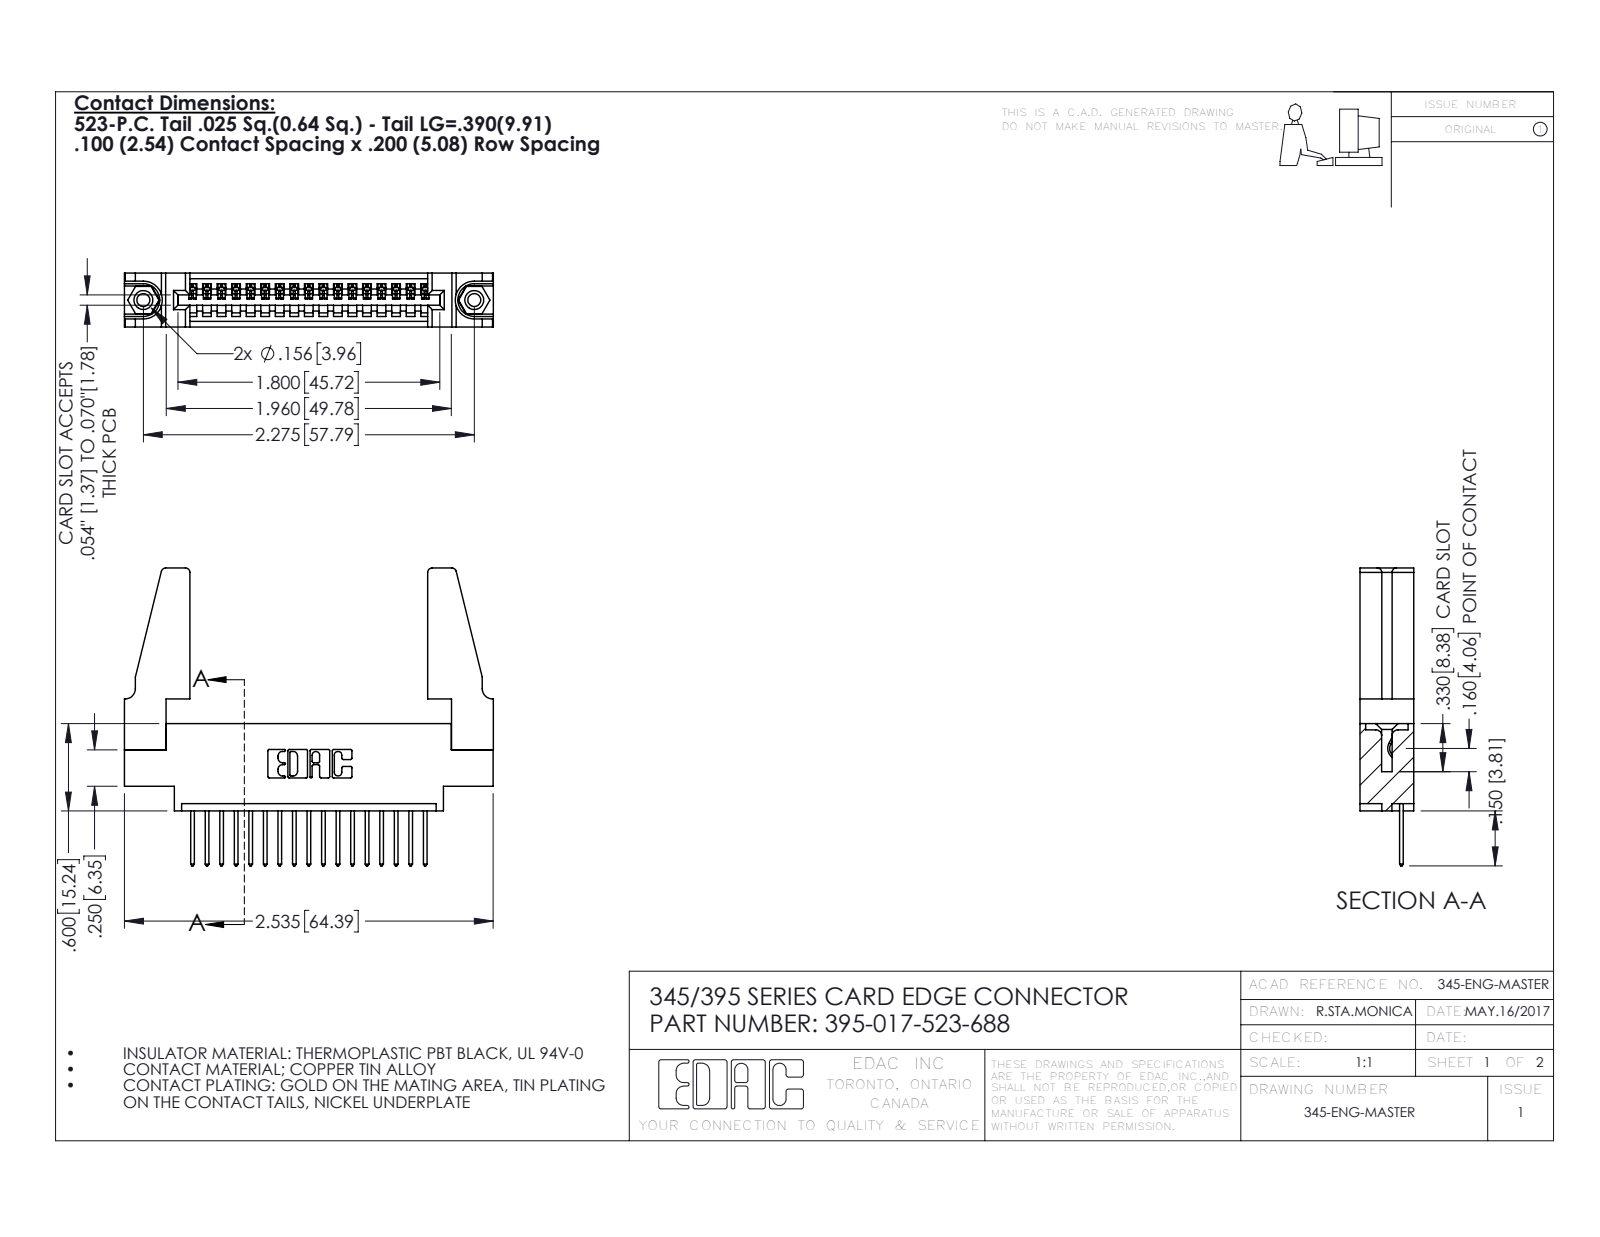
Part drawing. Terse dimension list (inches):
name: 345-292-001_345-293-123; 395-017-523-688; 345-220-078_345-220-088; 345-250-001_345-250-001-102 (+1 more)
written by: SolidWorks 2016 (CONFIG_CONTROL_DESIGN)
unit: in
bodies: 22 solids, 1240 faces (836 planar, 388 cylindrical, 16 other)
size: 2.536 × 2.047 × 0.37
volume: 0.552 in³; area: 16.48 in²
holes: 2× ⌀0.089, 2× ⌀0.125, 2× ⌀0.156, 1× ⌀0.064
bosses: 2× ⌀0.155
rounds: 34× R0.006, 34× R0.01, 22× R0.01, 8× R0.03, 6× R0.007, 6× R0.031, 3× R0.026, 2× R0.031
face distances: 0.37, 0.072, 0.298, 0.2, 0.098, 0.272, 0.025, 0.225, 0.15, 0.148
hole spacings: 0.27, 2.041, 2.275
